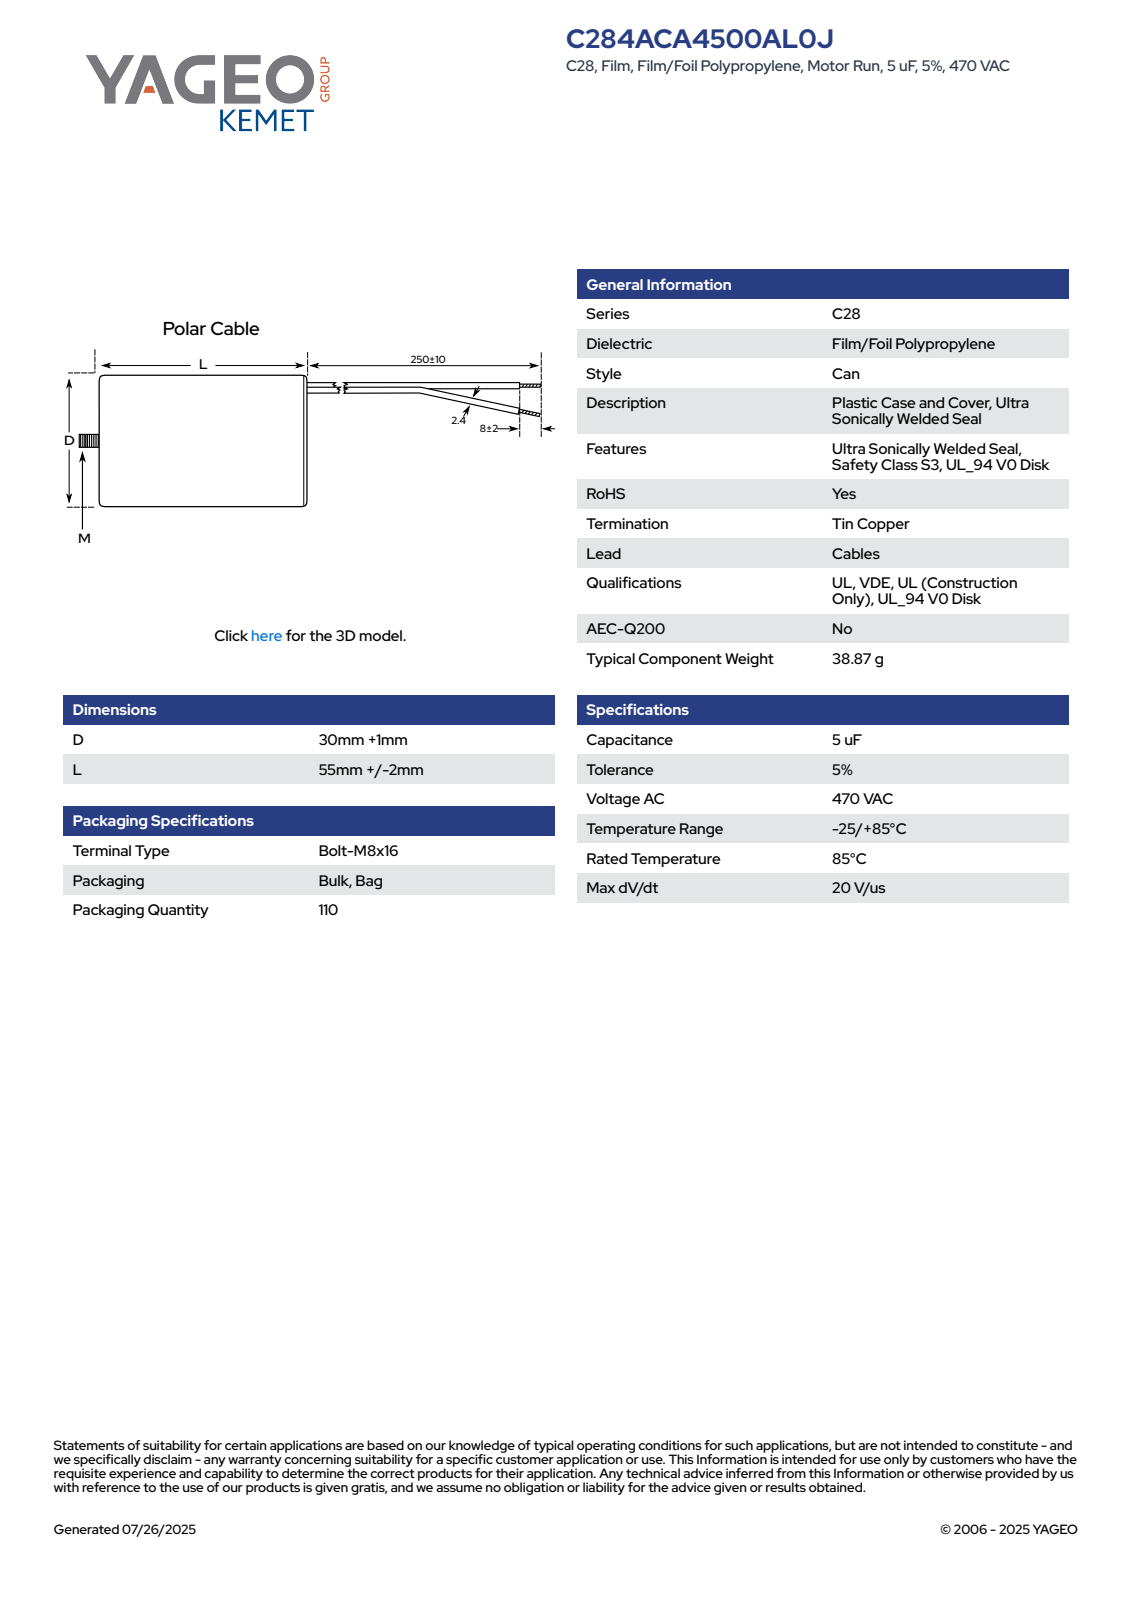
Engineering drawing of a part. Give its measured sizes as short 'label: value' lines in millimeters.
name: CFM_C28P_30X55_D31L57
written by: SolidWorks 2021 (AUTOMOTIVE_DESIGN)
unit: mm
bodies: 1 solid, 76 faces (26 planar, 15 cylindrical, 35 other)
size: 67 × 31.01 × 31
volume: 42 339 mm³; area: 7 399 mm²
holes: 1× ⌀27
bosses: 1× ⌀31, 1× ⌀8
rounds: 1× R15.51
face distances: 55, 57, 2, 10, 65, 67
